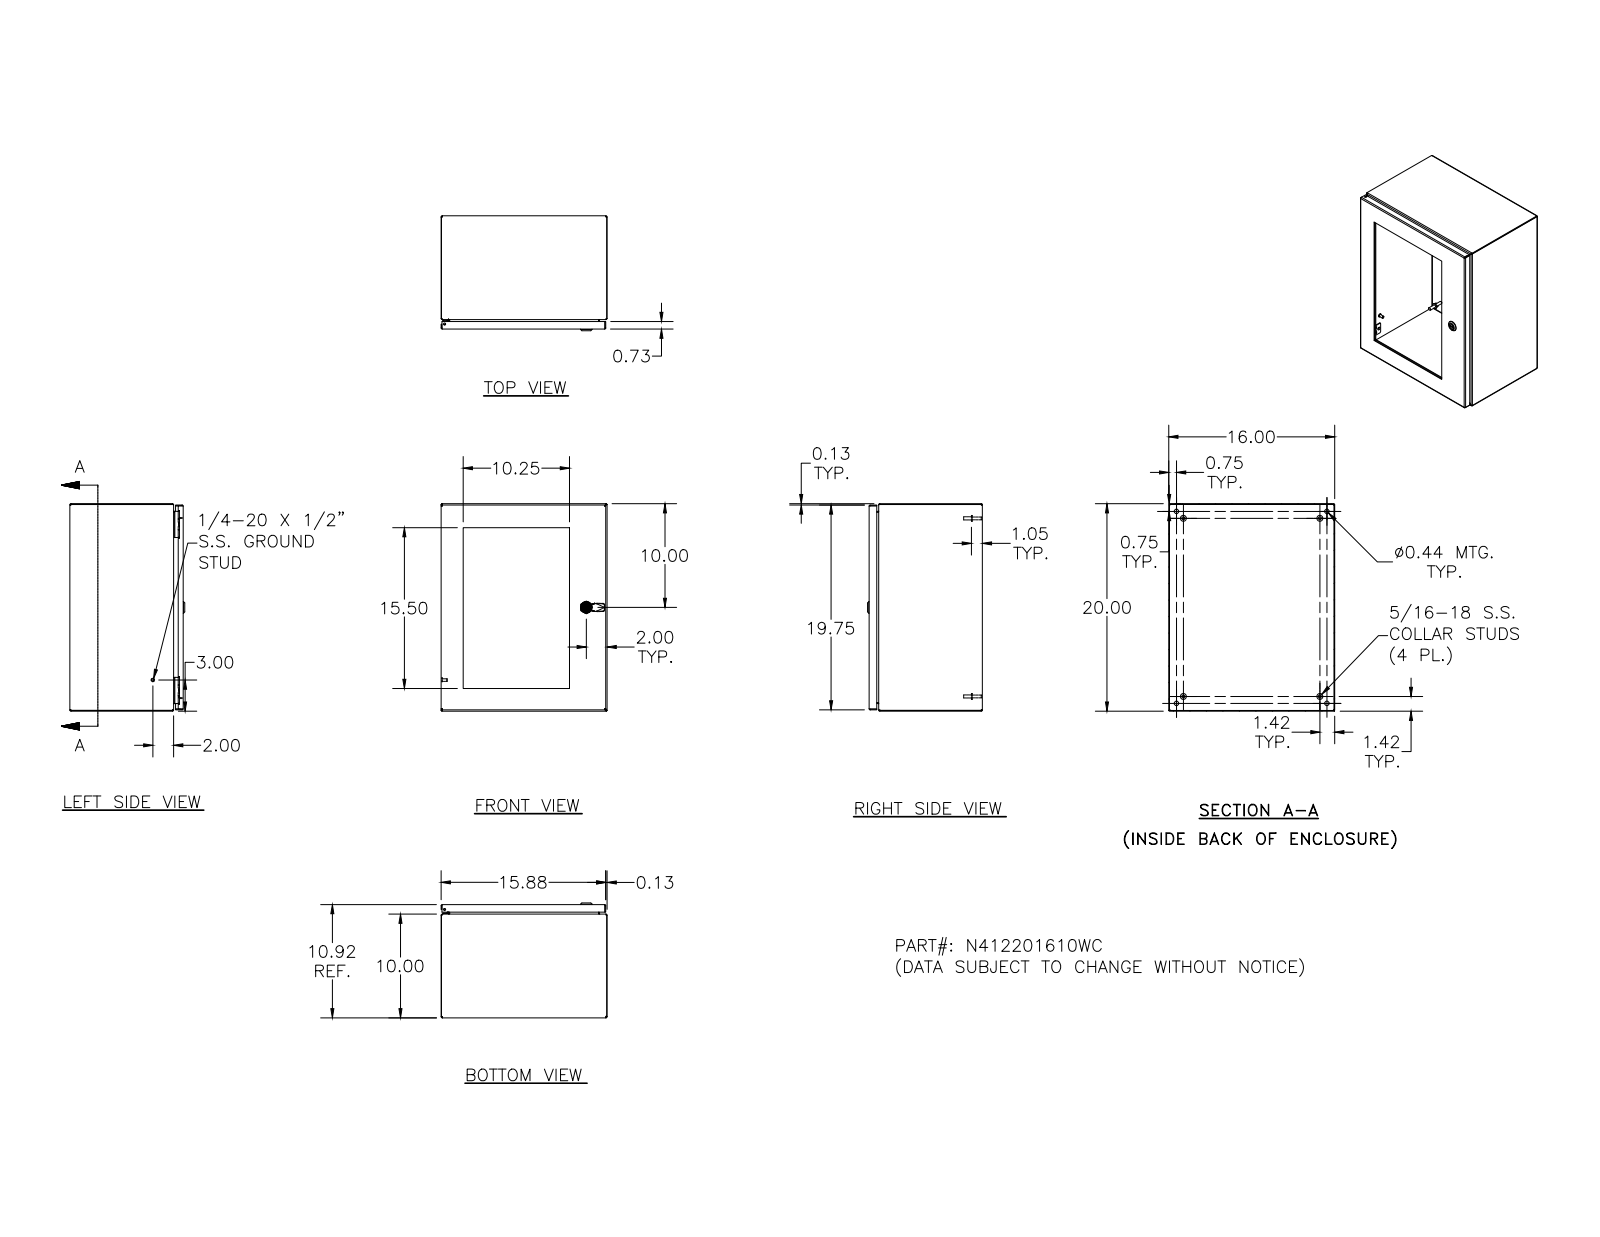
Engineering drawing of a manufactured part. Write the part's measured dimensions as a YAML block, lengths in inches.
part_name: "N412201610WC"
step_written_by: "SolidWorks 2018 (AUTOMOTIVE_DESIGN)"
units: inches
bodies: {solids: 65, faces: 1955, planar: 731, cylindrical: 609, other: 615}
overall_size: [20, 16, 11.075]
volume: 150.9
surface_area: 3244
round_holes:
  - {diameter: 0.156, count: 16}
  - {diameter: 0.281, count: 14}
  - {diameter: 0.188, count: 5}
  - {diameter: 0.093, count: 4}
  - {diameter: 0.152, count: 4}
  - {diameter: 0.167, count: 4}
  - {diameter: 0.172, count: 4}
  - {diameter: 0.437, count: 4}
  - {diameter: 0.187, count: 1}
  - {diameter: 0.197, count: 1}
  - {diameter: 0.315, count: 1}
  - {diameter: 0.394, count: 1}
round_bosses_or_shafts:
  - {diameter: 0.337, count: 14}
  - {diameter: 0.19, count: 14}
  - {diameter: 0.25, count: 10}
  - {diameter: 0.563, count: 4}
  - {diameter: 0.36, count: 4}
  - {diameter: 0.32, count: 4}
  - {diameter: 0.3, count: 4}
  - {diameter: 0.275, count: 4}
partial_cylinders:
  - {radius: 0.031, count: 34}
  - {radius: 0.012, count: 30}
  - {radius: 0.05, count: 26}
  - {radius: 0.105, count: 24}
  - {radius: 0.016, count: 18}
  - {radius: 0.125, count: 16}
  - {radius: 0.02, count: 13}
  - {radius: 0.032, count: 8}
face_to_face_distances: [0.074, 10.843, 15.926, 10.769, 19.926, 16, 15.852, 0.25, 10.593, 10.519]
hole_center_spacings: [4, 8, 12.176, 16, 6.221, 8.585, 10.035, 11.5]
